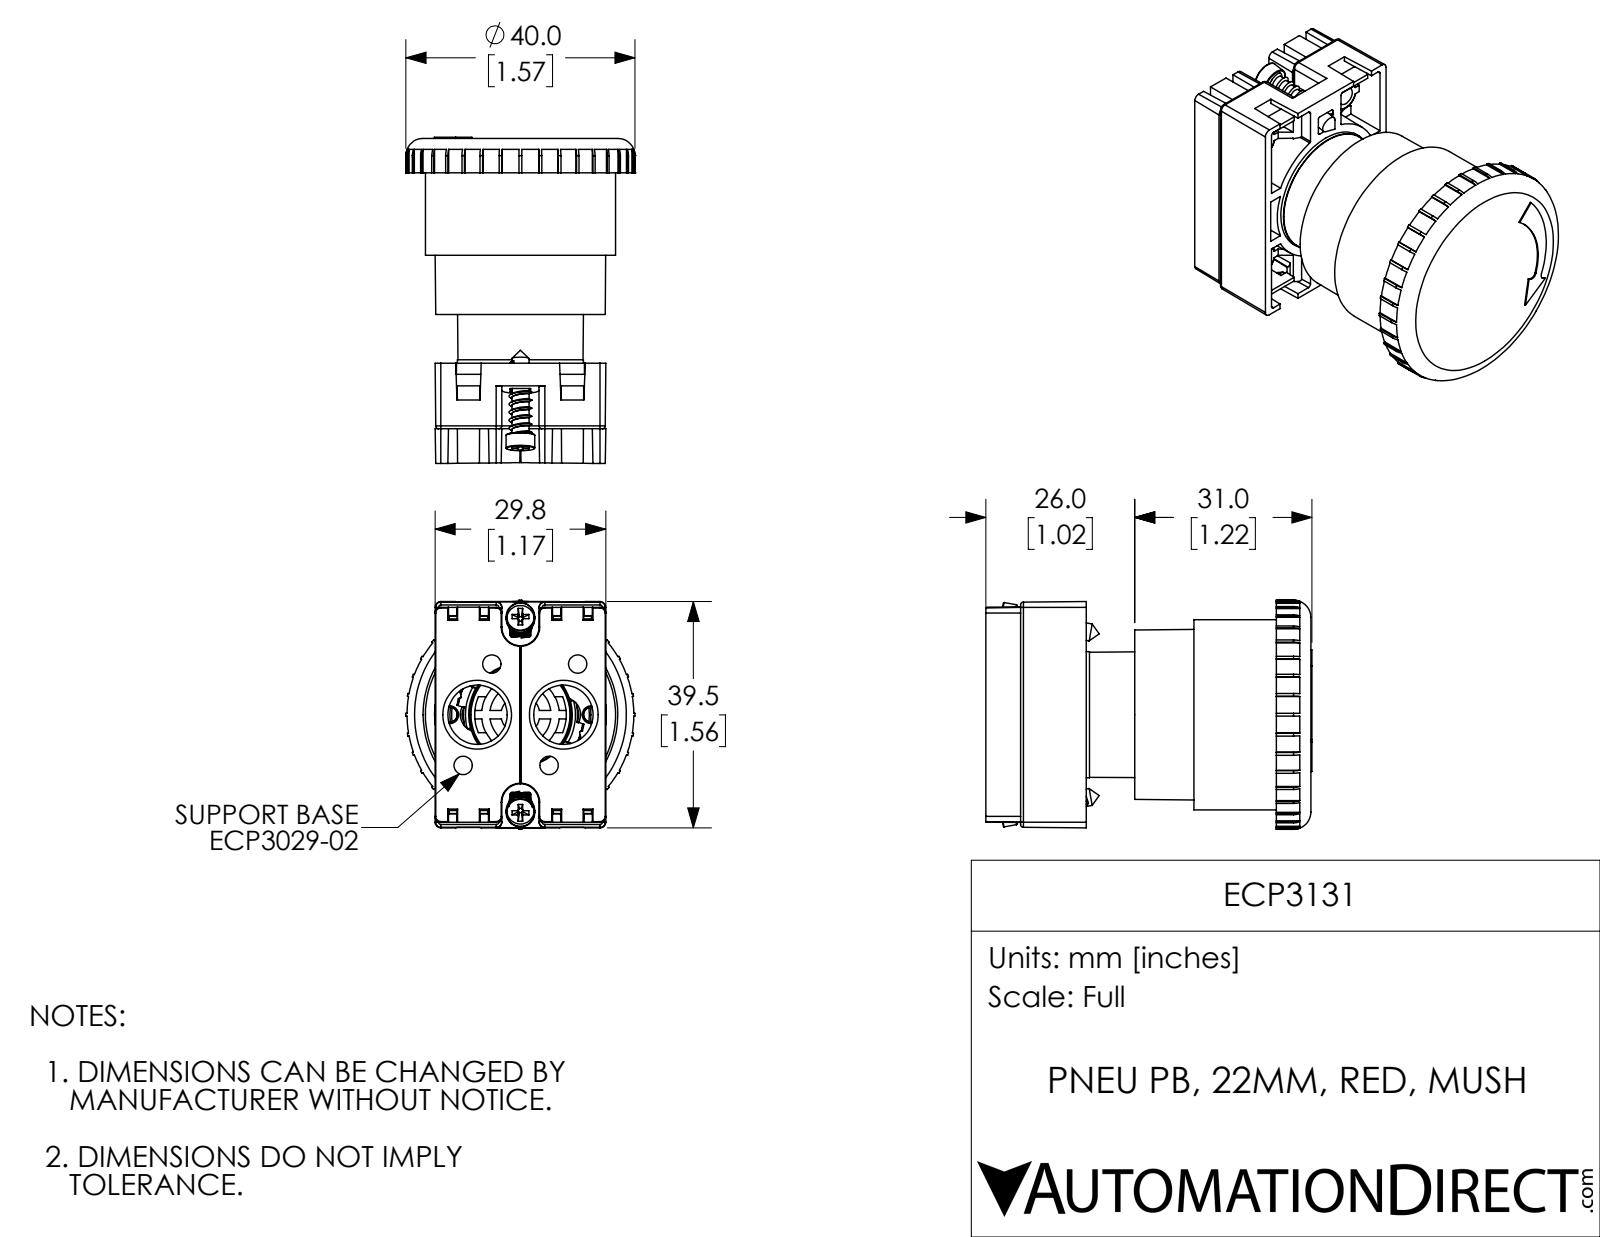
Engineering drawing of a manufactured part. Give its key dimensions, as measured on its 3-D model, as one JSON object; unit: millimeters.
{"part_name": "ECP3131", "step_written_by": "SolidWorks 2017 (AUTOMOTIVE_DESIGN)", "units": "millimeters", "bodies": {"solids": 7, "faces": 1004, "planar": 484, "cylindrical": 238, "other": 282}, "overall_size": [56.9, 40, 40], "volume_mm3": 19660, "surface_area_mm2": 25250, "round_holes": [[2.1, 4], [10.3, 2], [2.6, 1], [10.7, 1], [17.7, 1], [19, 1], [19.2, 1], [30, 1], [37, 1]], "round_bosses_or_shafts": [[5, 2], [3, 2], [39.6, 1], [33.2, 1], [22.5, 1], [22, 1], [13.6, 1]], "partial_cylinders_radius": [[0.5, 18], [0.2, 8], [0.3, 8], [1, 6], [0.2, 4], [0.2, 2], [3, 2], [3.3, 2]], "face_to_face_distances": [50.7, 1.5, 49.2, 4.5, 1.7, 18.2, 39.2, 37.7, 11.5, 14.9], "hole_center_spacings": [7.7, 13.7, 20.8, 7.5, 12, 24.7, 27.5, 15]}
